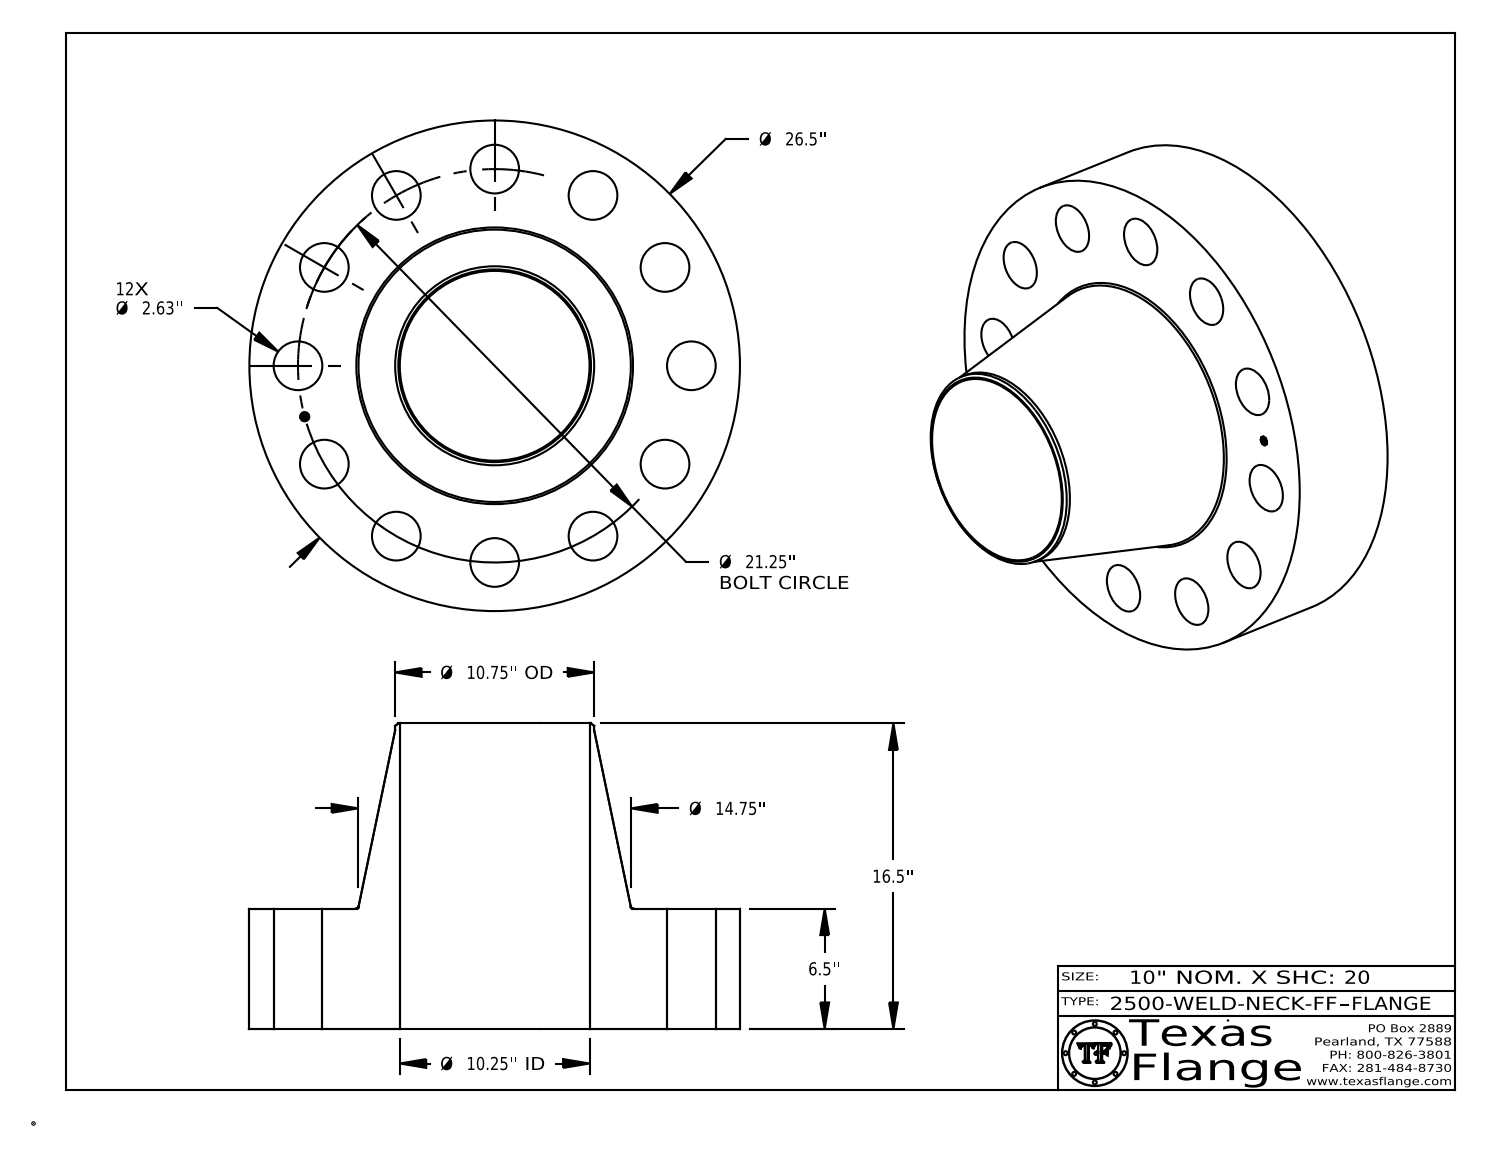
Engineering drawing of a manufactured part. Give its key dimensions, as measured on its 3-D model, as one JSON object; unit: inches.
{"part_name": "2500-WELD-NECK-FF", "step_written_by": "CATIA V5 STEP AP214 (AUTOMOTIVE_DESIGN)", "units": "inches", "bodies": {"solids": 1, "faces": 424, "planar": 368, "cylindrical": 50, "other": 6}, "overall_size": [26.5, 26.5, 16.5], "volume_in3": 3073, "surface_area_in2": 2847, "round_holes": [[2.63, 12], [0.495, 1], [10.25, 1]], "round_bosses_or_shafts": [[0.03, 8], [26.5, 1], [10.75, 1], [0.39, 1]], "face_to_face_distances": [6.5, 16.5, 10, 6.485, 0.015, 10.015, 0.148, 0.144, 0.027, 0.096], "hole_center_spacings": [10.625, 5.5, 18.403, 15.026, 20.526, 15.026, 20.526, 21.25]}
